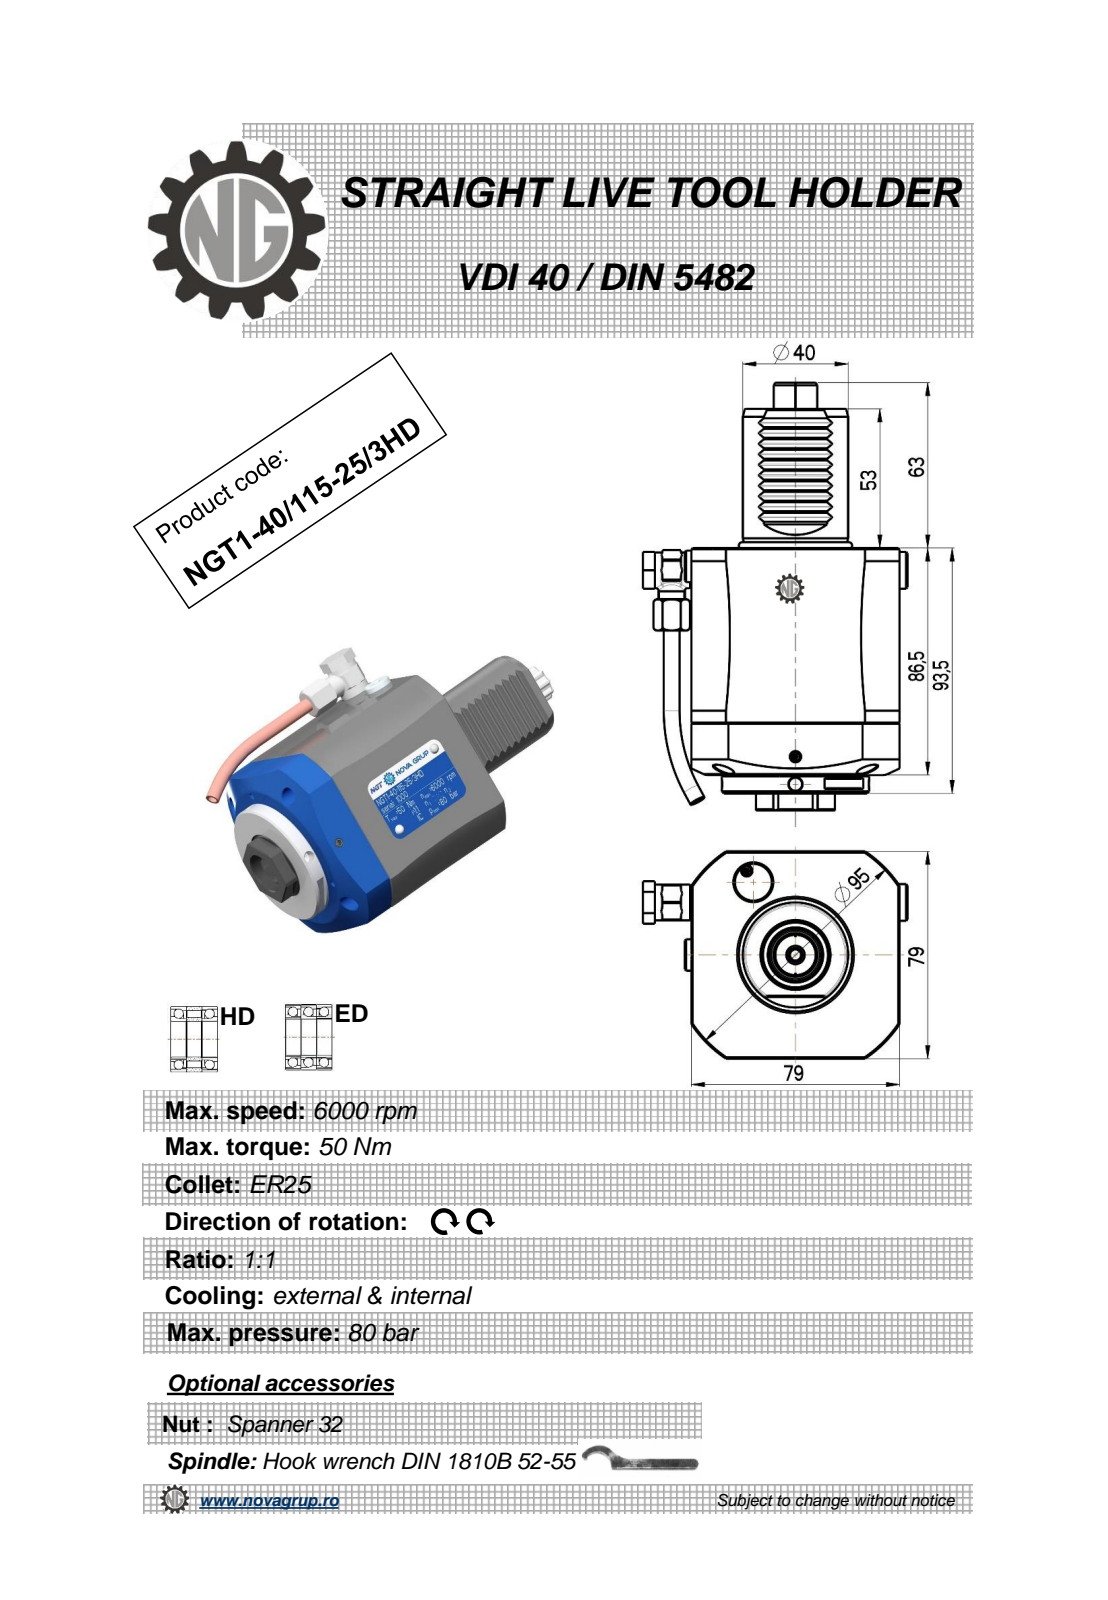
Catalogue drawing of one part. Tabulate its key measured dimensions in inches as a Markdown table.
| quantity | value |
| --- | --- |
| part name | NGT1_40_115_25_3HD |
| STEP written by | PRO/ENGINEER BY PARAMETRIC TECHNOLOGY CORPORATION, 2010280 (CONFIG_CONTROL_DESIGN) |
| units | inches |
| bodies | 3 solids, 431 faces (147 planar, 146 cylindrical, 138 other) |
| overall size | 6.417 × 3.953 × 3.11 |
| volume | 36.08 in³ |
| surface area | 81.81 in² |
| round holes (diameter × count) | 0.157 × 3, 0.197 × 2, 0.118 × 1, 0.165 × 1, 0.209 × 1, 0.236 × 1, 0.244 × 1, 0.354 × 1, 0.394 × 1, 0.433 × 1, 0.709 × 1, 1.043 × 1 |
| round bosses / shafts (diameter × count) | 2.205 × 1, 1.575 × 1, 0.551 × 1, 0.535 × 1, 0.512 × 1, 0.472 × 1, 0.394 × 1, 0.335 × 1 |
| partial cylindrical surfaces (radius × count) | 0.119 × 18, 0.012 × 10, 0.016 × 6, 0.02 × 4, 0.266 × 1, 0.303 × 1, 0.325 × 1, 0.591 × 1 |
| main face-to-face distances | 3.11, 3.406, 0.276, 3.681, 2.087, 5.768, 5.492, 0.111, 0.334, 0.557 |
| hole center spacings | 0.016, 2.011, 2.026, 3.304 |
